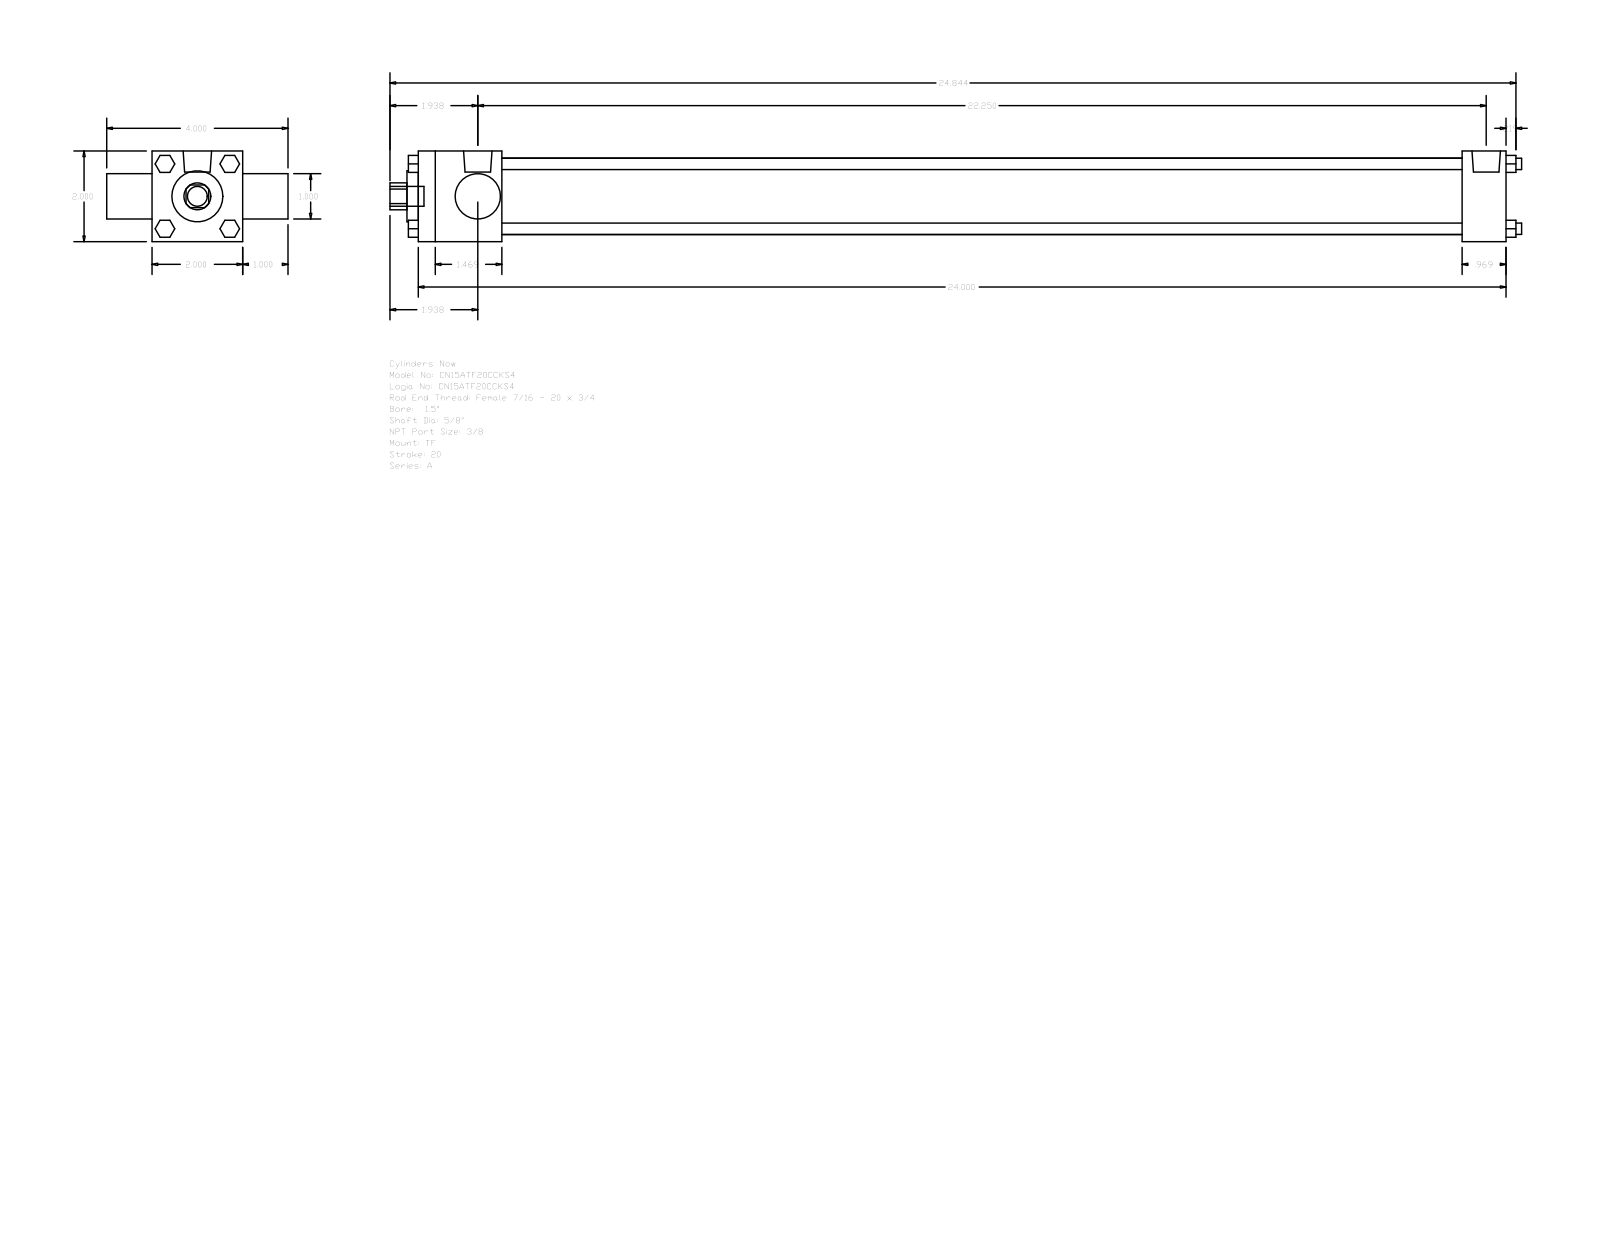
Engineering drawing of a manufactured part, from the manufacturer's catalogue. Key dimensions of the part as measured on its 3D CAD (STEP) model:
Part name (STEP PRODUCT): A_TF__0150_0.625
STEP written by: GSSL Pune (CONFIG_CONTROL_DESIGN)
Units: millimetres
Bodies: 0 solids, 120 faces (92 planar, 28 cylindrical, 0 other)
Overall size (bounding box): 634.21 × 101.6 × 50.8
Round holes (diameter × count): ⌀15.88 ×1, ⌀25.4 ×1, ⌀28.57 ×1, ⌀42.93 ×1
Round bosses / shafts (diameter × count): ⌀6.35 ×4, ⌀5.56 ×3, ⌀15.93 ×2, ⌀11.11 ×1
Partial cylindrical surfaces — rounded edges, fillets, slot ends (radius × count): R7.54 ×1
Main face-to-face distances: 50.8, 609.6, 25.4, 76.2, 46.83, 584.99, 538.16, 562.77, 24.61, 9.52
